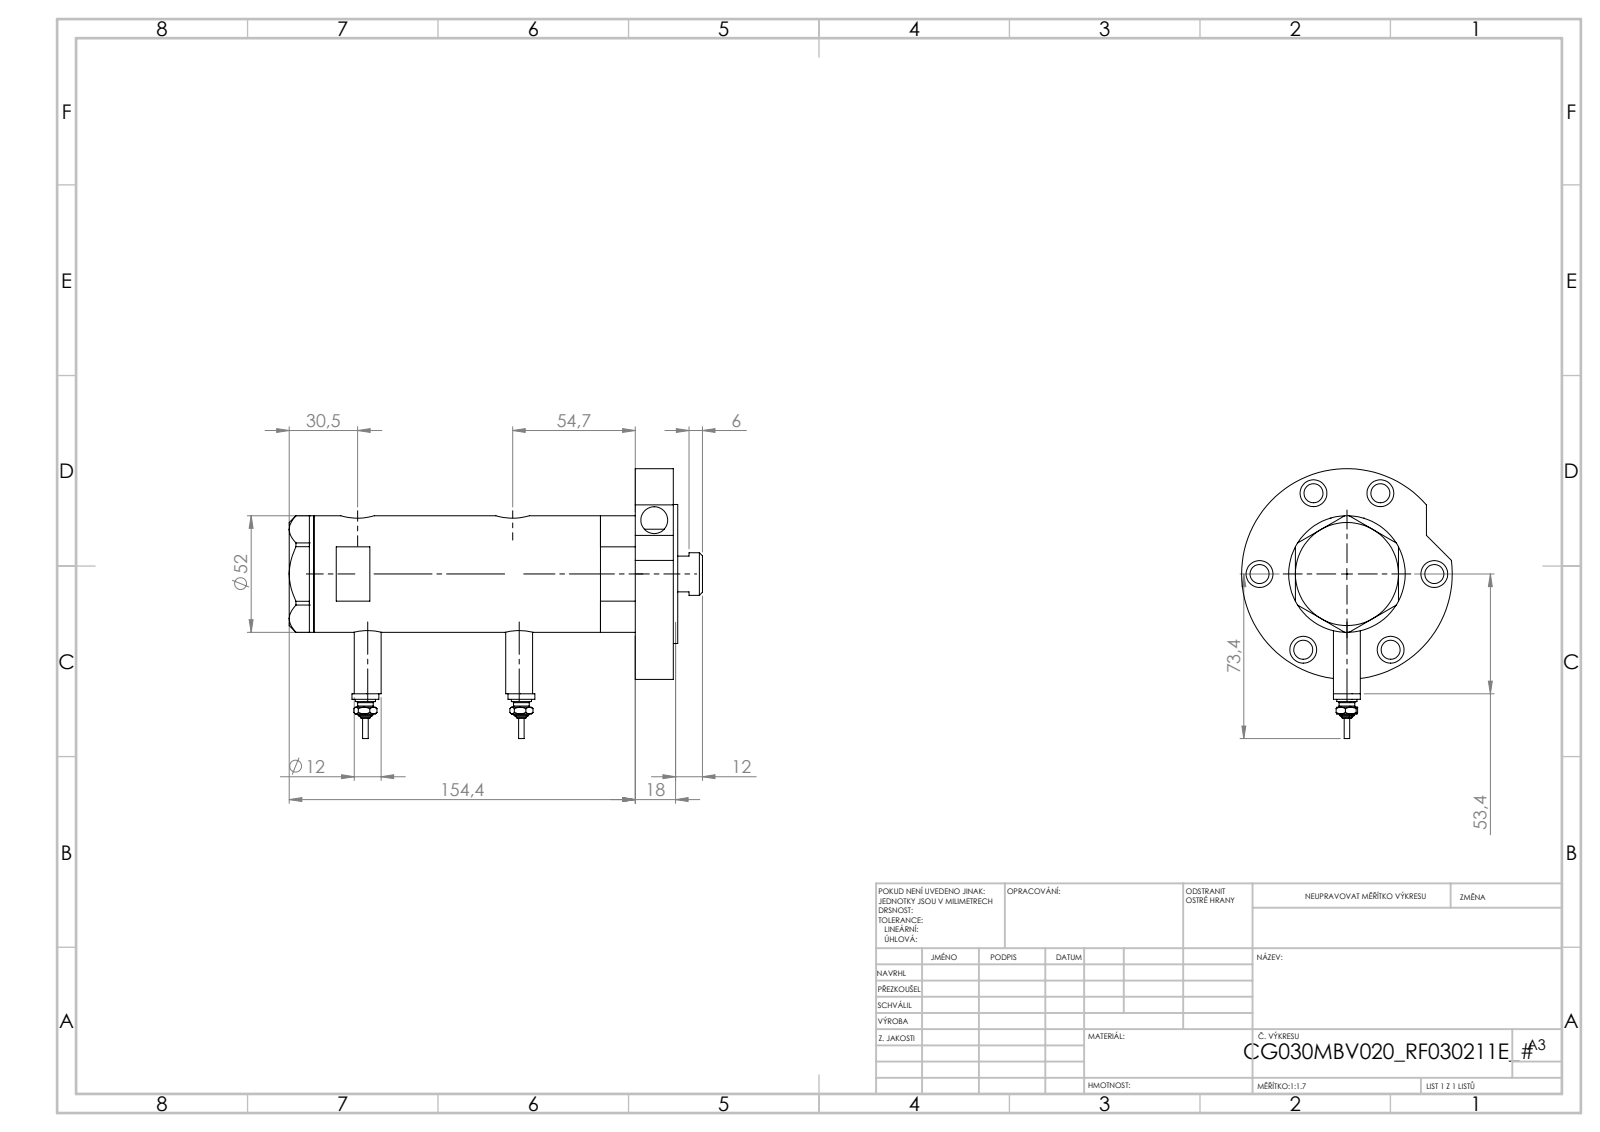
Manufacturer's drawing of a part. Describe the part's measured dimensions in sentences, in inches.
The part is named "V270CG_BACK; V270CG_FRONT; V270CG_VC; V270CG_RF211E (+2 more)". Its 3-D file was written by "SolidWorks 2019 (CONFIG_CONTROL_DESIGN)". It is 7 solids with 270 faces: 104 planar, 102 cylindrical and 64 other. Overall it measures 7.26 by 4.74 by 3.701 inches. Its volume is 26.04 cubic inches and its surface area 161.2 square inches. Round holes: 7 of diameter 0.472, 6 of diameter 0.335, 2 of diameter 0.383, 2 of diameter 0.492, 2 of diameter 0.591, 1 of diameter 0.256, 1 of diameter 0.787, 1 of diameter 0.846, 1 of diameter 1.181, 1 of diameter 1.299, 1 of diameter 1.575, 1 of diameter 1.732. Round bosses or shafts: 4 of diameter 0.472, 2 of diameter 0.354, 2 of diameter 0.276, 2 of diameter 0.177, 2 of diameter 0.098, 1 of diameter 3.701, 1 of diameter 2.441, 1 of diameter 2.047. The main face-to-face distances are 0.669, 5.646, 6.315, 0.079, 6.394, 3.602, 2.043, 2.713, 0.433, 6.827. The hole center spacings are 1.535, 1.706, 2.553, 2.659, 2.754, 3.064, 0.114, 0.177.
